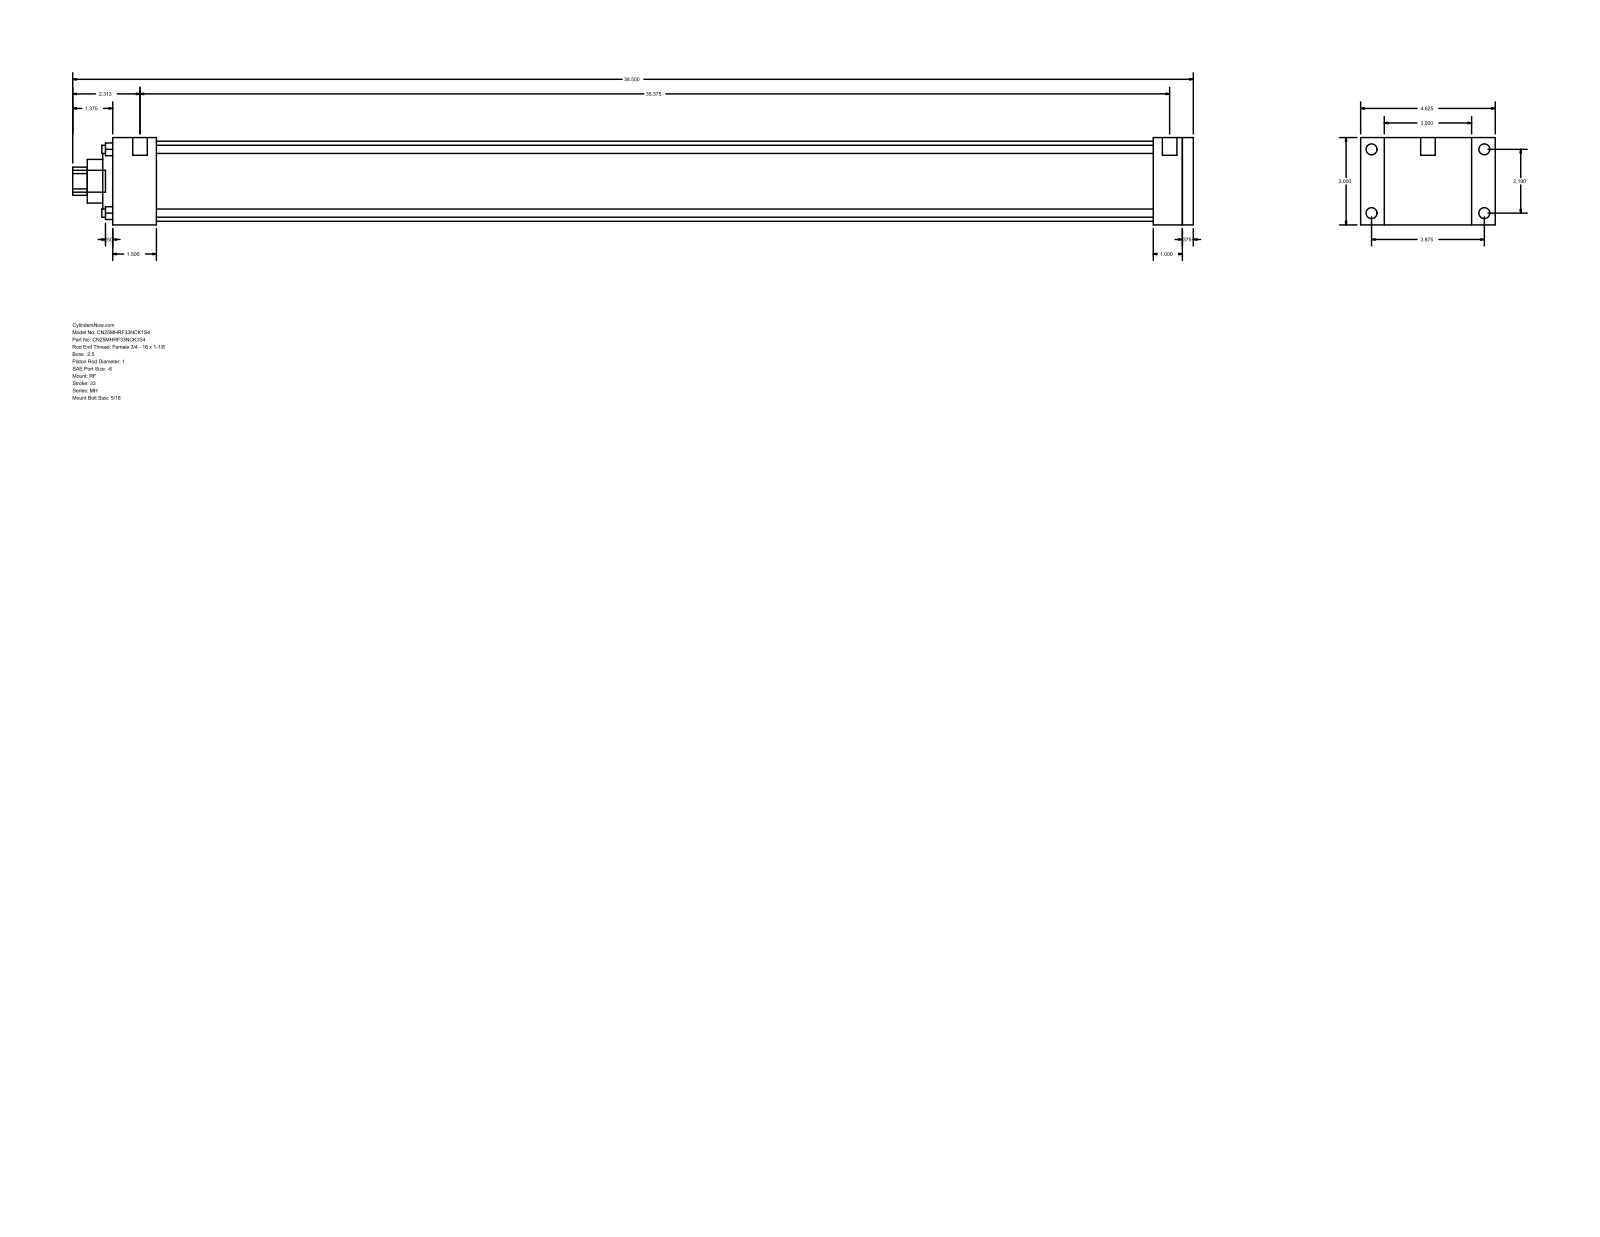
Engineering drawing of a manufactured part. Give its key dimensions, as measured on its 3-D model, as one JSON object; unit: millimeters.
{"part_name": "MH_RF__0250_1", "step_written_by": "GSSL Pune (CONFIG_CONTROL_DESIGN)", "units": "millimeters", "bodies": {"solids": 0, "faces": 94, "planar": 65, "cylindrical": 29, "other": 0}, "overall_size": [977.9, 117.47, 76.2], "round_holes": [[7.14, 4], [25.4, 1], [38.1, 1], [60.33, 1], [69.85, 1]], "round_bosses_or_shafts": [[9.53, 4], [5.56, 4], [12.7, 2], [19.05, 1]], "partial_cylinders_radius": [[12.29, 1]], "face_to_face_distances": [76.2, 9.52, 942.98, 933.46, 25.4, 34.92, 908.06, 38.11, 869.95, 895.35], "hole_center_spacings": [39.33, 55.62, 78.66]}
